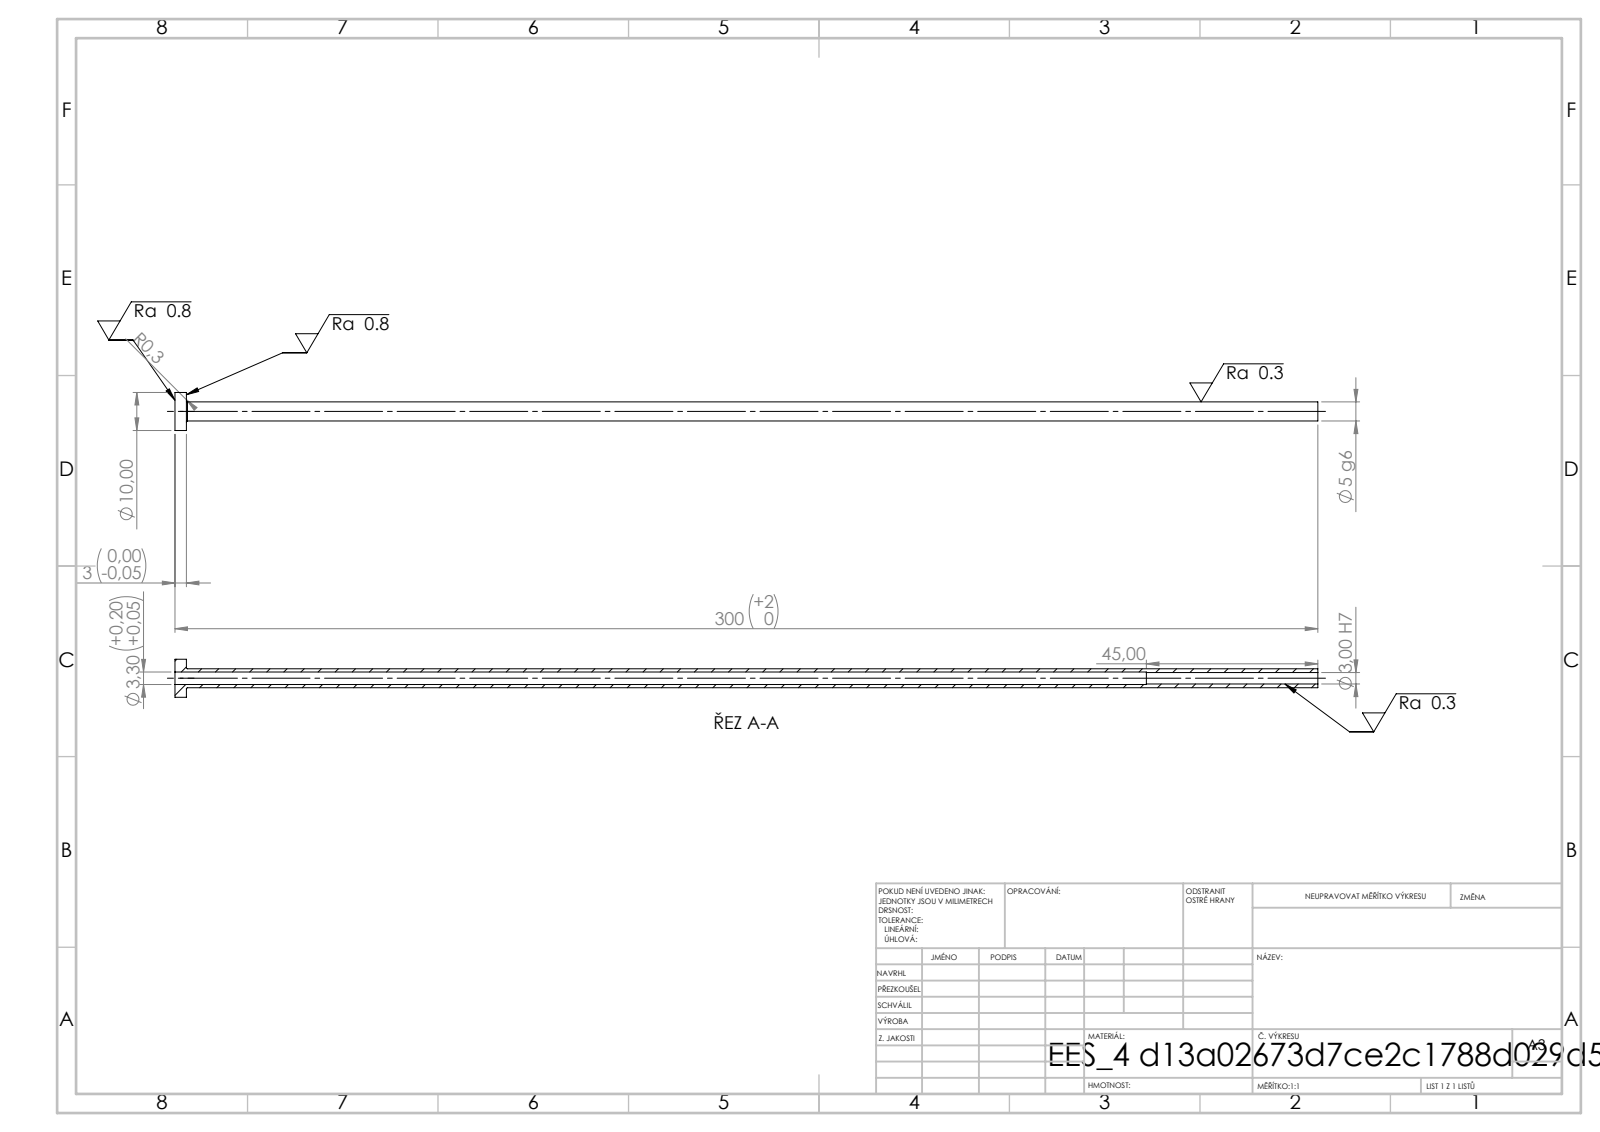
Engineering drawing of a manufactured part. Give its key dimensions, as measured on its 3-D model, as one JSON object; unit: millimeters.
{"step_written_by": "SolidWorks 2019 (CONFIG_CONTROL_DESIGN)", "units": "millimeters", "bodies": {"solids": 1, "faces": 14, "planar": 4, "cylindrical": 8, "other": 2}, "overall_size": [300, 10, 10], "volume_mm3": 3568, "surface_area_mm2": 7968, "round_holes": [[3, 1], [3.3, 1]], "round_bosses_or_shafts": [[10, 1], [5, 1]], "face_to_face_distances": [3, 300, 297, 255, 252, 45]}
